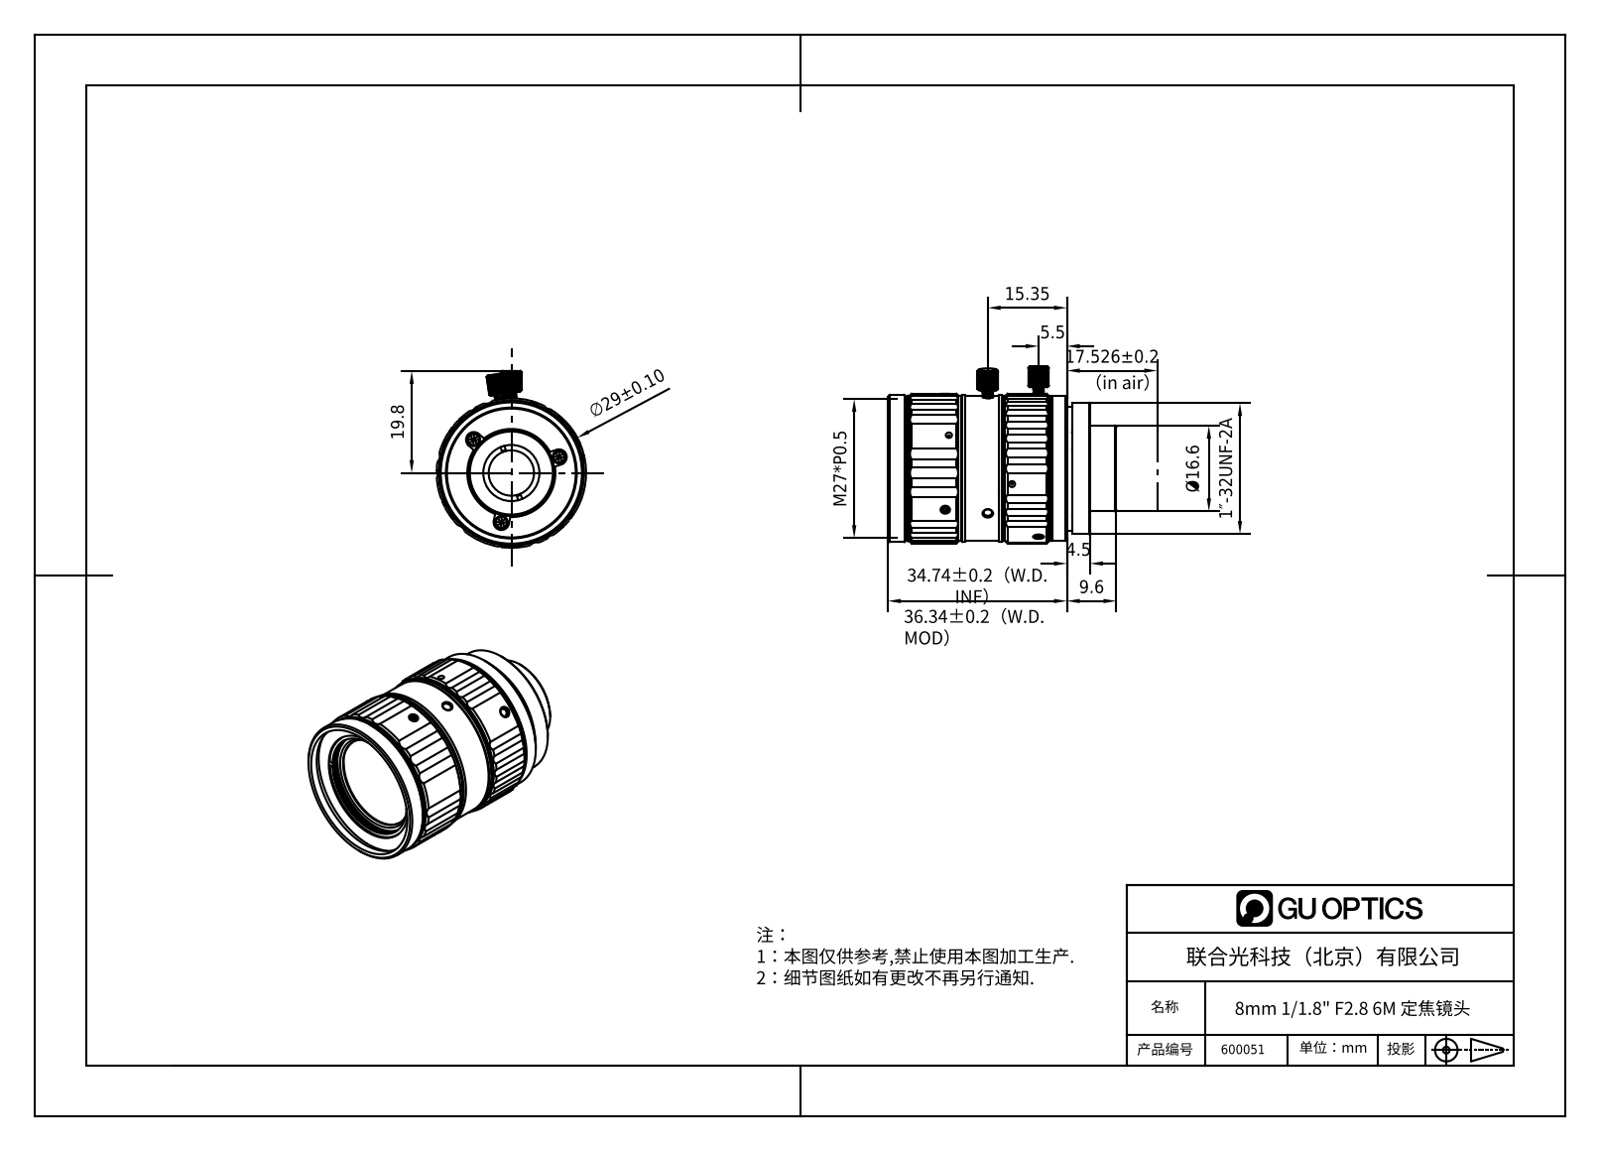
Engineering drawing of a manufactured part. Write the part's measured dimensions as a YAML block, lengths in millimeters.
part_name: "600051"
step_written_by: "SolidWorks 2020 (CONFIG_CONTROL_DESIGN)"
units: millimeters
bodies: {solids: 11, faces: 1205, planar: 282, cylindrical: 648, other: 275}
overall_size: [44.34, 33.88, 29]
volume: 23393
surface_area: 8203
round_holes:
  - {diameter: 1.6, count: 7}
  - {diameter: 1.22, count: 6}
  - {diameter: 1.65, count: 3}
  - {diameter: 1.7, count: 3}
  - {diameter: 2, count: 2}
  - {diameter: 1.62, count: 1}
  - {diameter: 8.8, count: 1}
  - {diameter: 10.89, count: 1}
  - {diameter: 11.9, count: 1}
  - {diameter: 16.7, count: 1}
  - {diameter: 18.1, count: 1}
  - {diameter: 20.3, count: 1}
round_bosses_or_shafts:
  - {diameter: 1.6, count: 8}
  - {diameter: 2.5, count: 3}
  - {diameter: 1.2, count: 3}
  - {diameter: 1.2, count: 3}
  - {diameter: 2, count: 2}
  - {diameter: 29, count: 1}
  - {diameter: 28.5, count: 1}
  - {diameter: 28.4, count: 1}
partial_cylinders:
  - {radius: 1.5, count: 25}
  - {radius: 2.3, count: 18}
  - {radius: 3.39, count: 6}
  - {radius: 1.11, count: 5}
  - {radius: 3.43, count: 4}
  - {radius: 0.82, count: 3}
  - {radius: 1, count: 3}
  - {radius: 1.01, count: 3}
face_to_face_distances: [1, 32.24, 36.74, 35.74, 1.5, 34.24, 2.5, 31.24, 2, 3.5]
hole_center_spacings: [16.88, 9.75, 9.74, 16.89]
